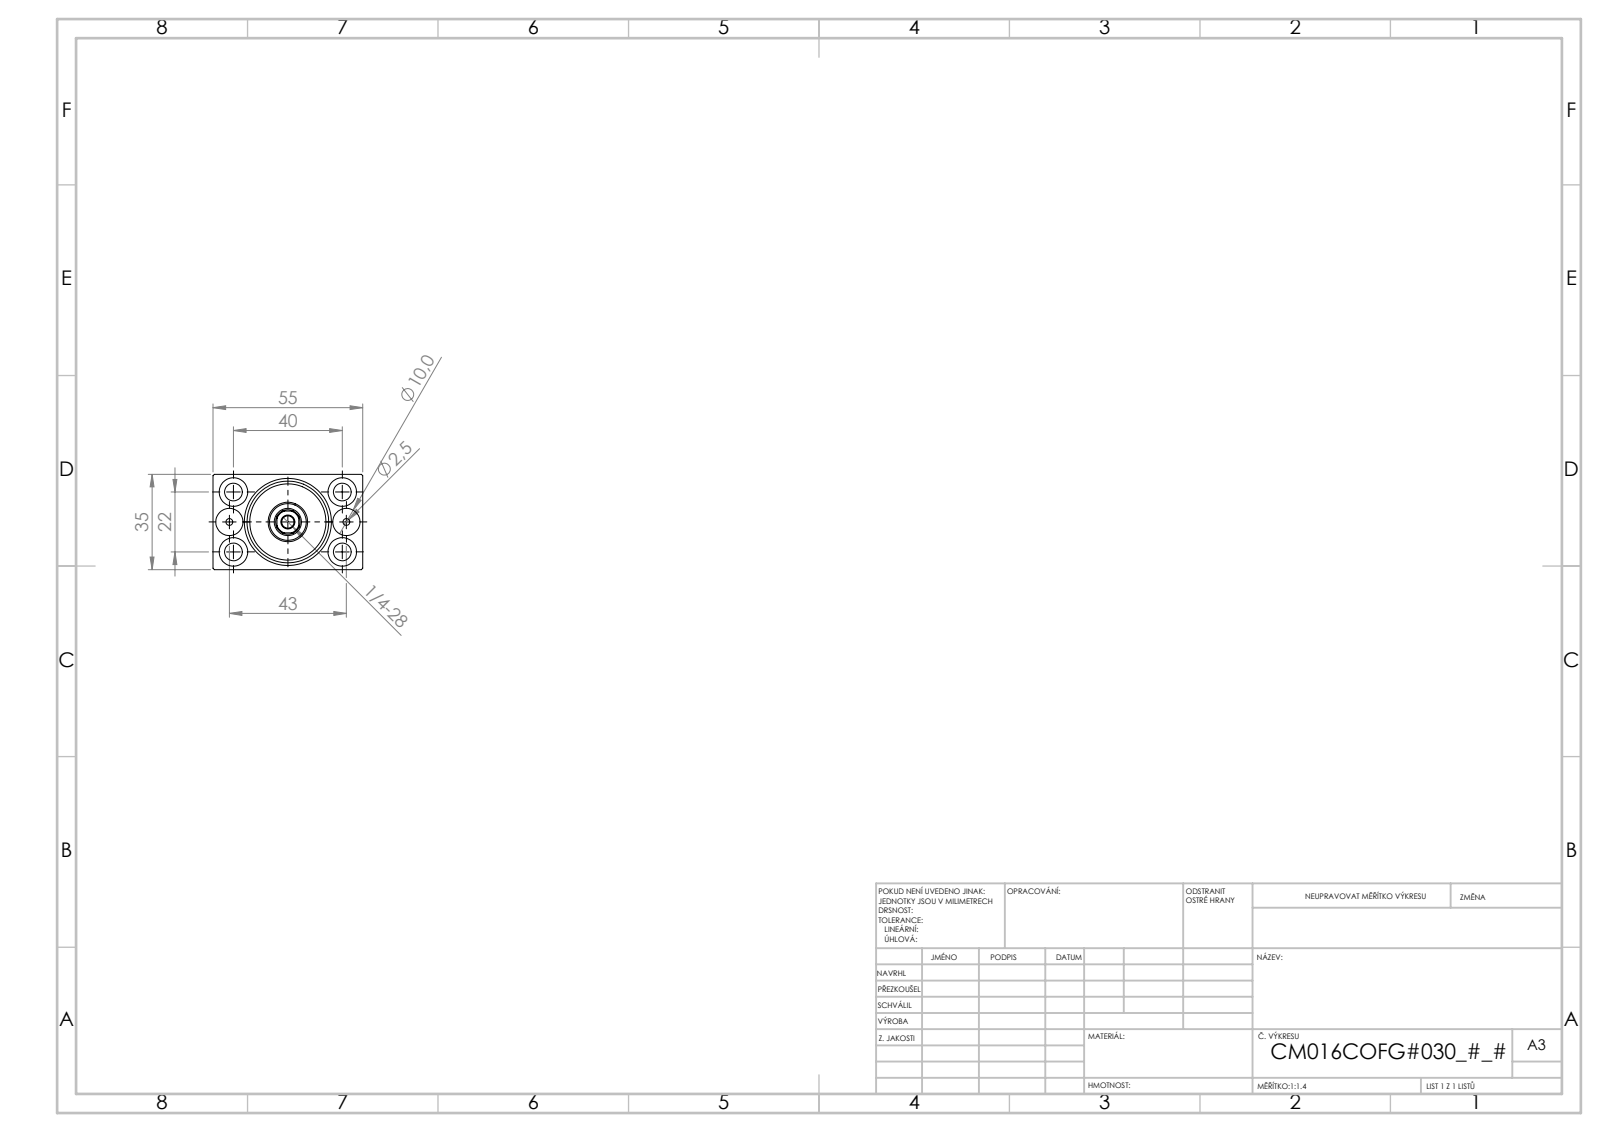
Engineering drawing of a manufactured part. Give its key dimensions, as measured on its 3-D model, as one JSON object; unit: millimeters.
{"part_name": "V450CM_VC_B; V450CM_C_VCP; V450CM_C_Body", "step_written_by": "SolidWorks 2019 (CONFIG_CONTROL_DESIGN)", "units": "millimeters", "bodies": {"solids": 3, "faces": 861, "planar": 409, "cylindrical": 58, "other": 394}, "overall_size": [85, 55, 35], "volume_mm3": 129437, "surface_area_mm2": 35806, "round_holes": [[6.5, 4], [10.5, 4], [10, 3], [2.5, 2], [4.5, 1], [13.5, 1], [14.5, 1], [16, 1], [18, 1], [30, 1]], "partial_cylinders_radius": [[4.5, 1]], "face_to_face_distances": [35, 55, 71, 5, 2, 76, 3, 66, 8, 79], "hole_center_spacings": [11.1, 22.83, 42.93, 21.5, 22, 40, 45.65, 43]}
